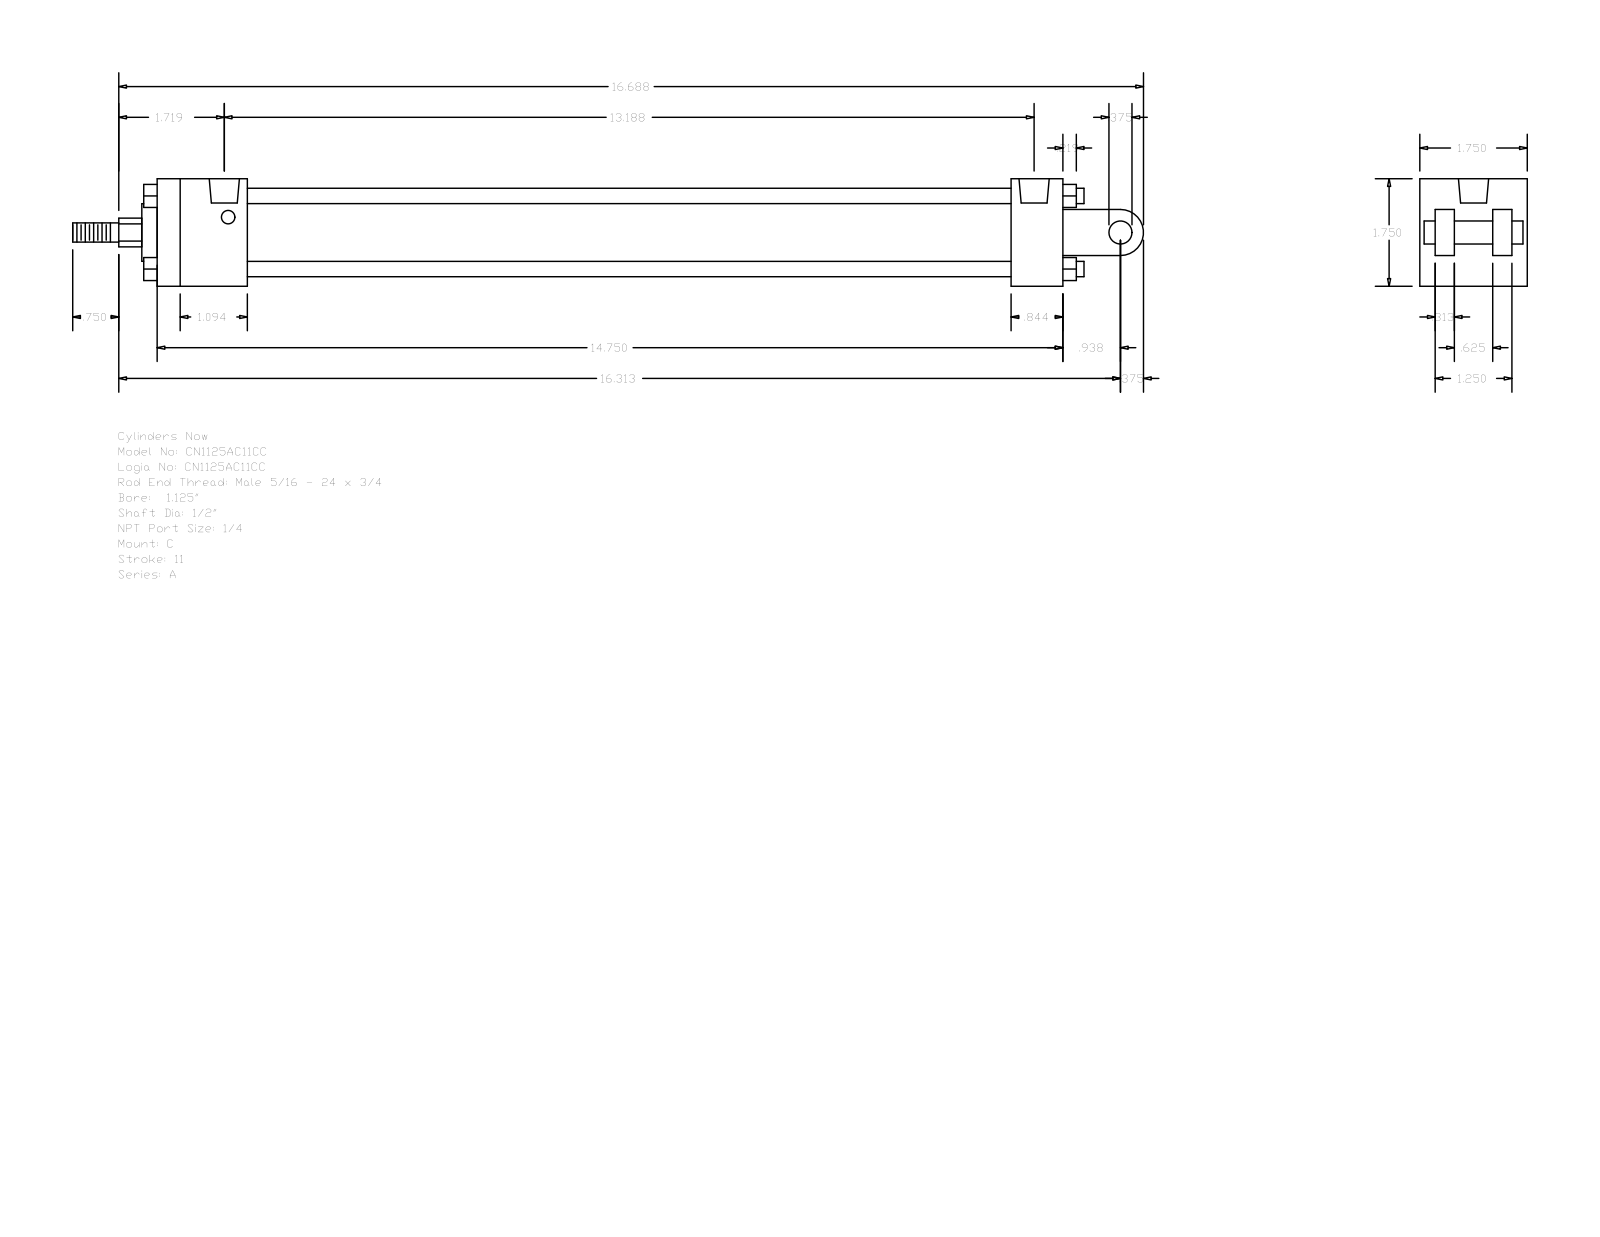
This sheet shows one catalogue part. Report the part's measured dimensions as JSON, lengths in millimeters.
{"part_name": "A_C__0112_0.5", "step_written_by": "GSSL Pune (CONFIG_CONTROL_DESIGN)", "units": "millimeters", "bodies": {"solids": 0, "faces": 135, "planar": 102, "cylindrical": 33, "other": 0}, "overall_size": [442.91, 44.45, 44.45], "round_holes": [[5.56, 4], [12.49, 2]], "round_bosses_or_shafts": [[6.35, 4], [31.88, 1], [23.81, 1], [12.7, 1], [9.53, 1], [7.94, 1]], "partial_cylinders_radius": [[5.94, 1], [9.53, 1]], "face_to_face_distances": [44.46, 6.35, 31.76, 14.29, 374.64, 30.17, 353.21, 21.43, 37.3, 315.91], "hole_center_spacings": [331.79, 1.58, 1.59, 333.37, 333.38, 334.96]}
